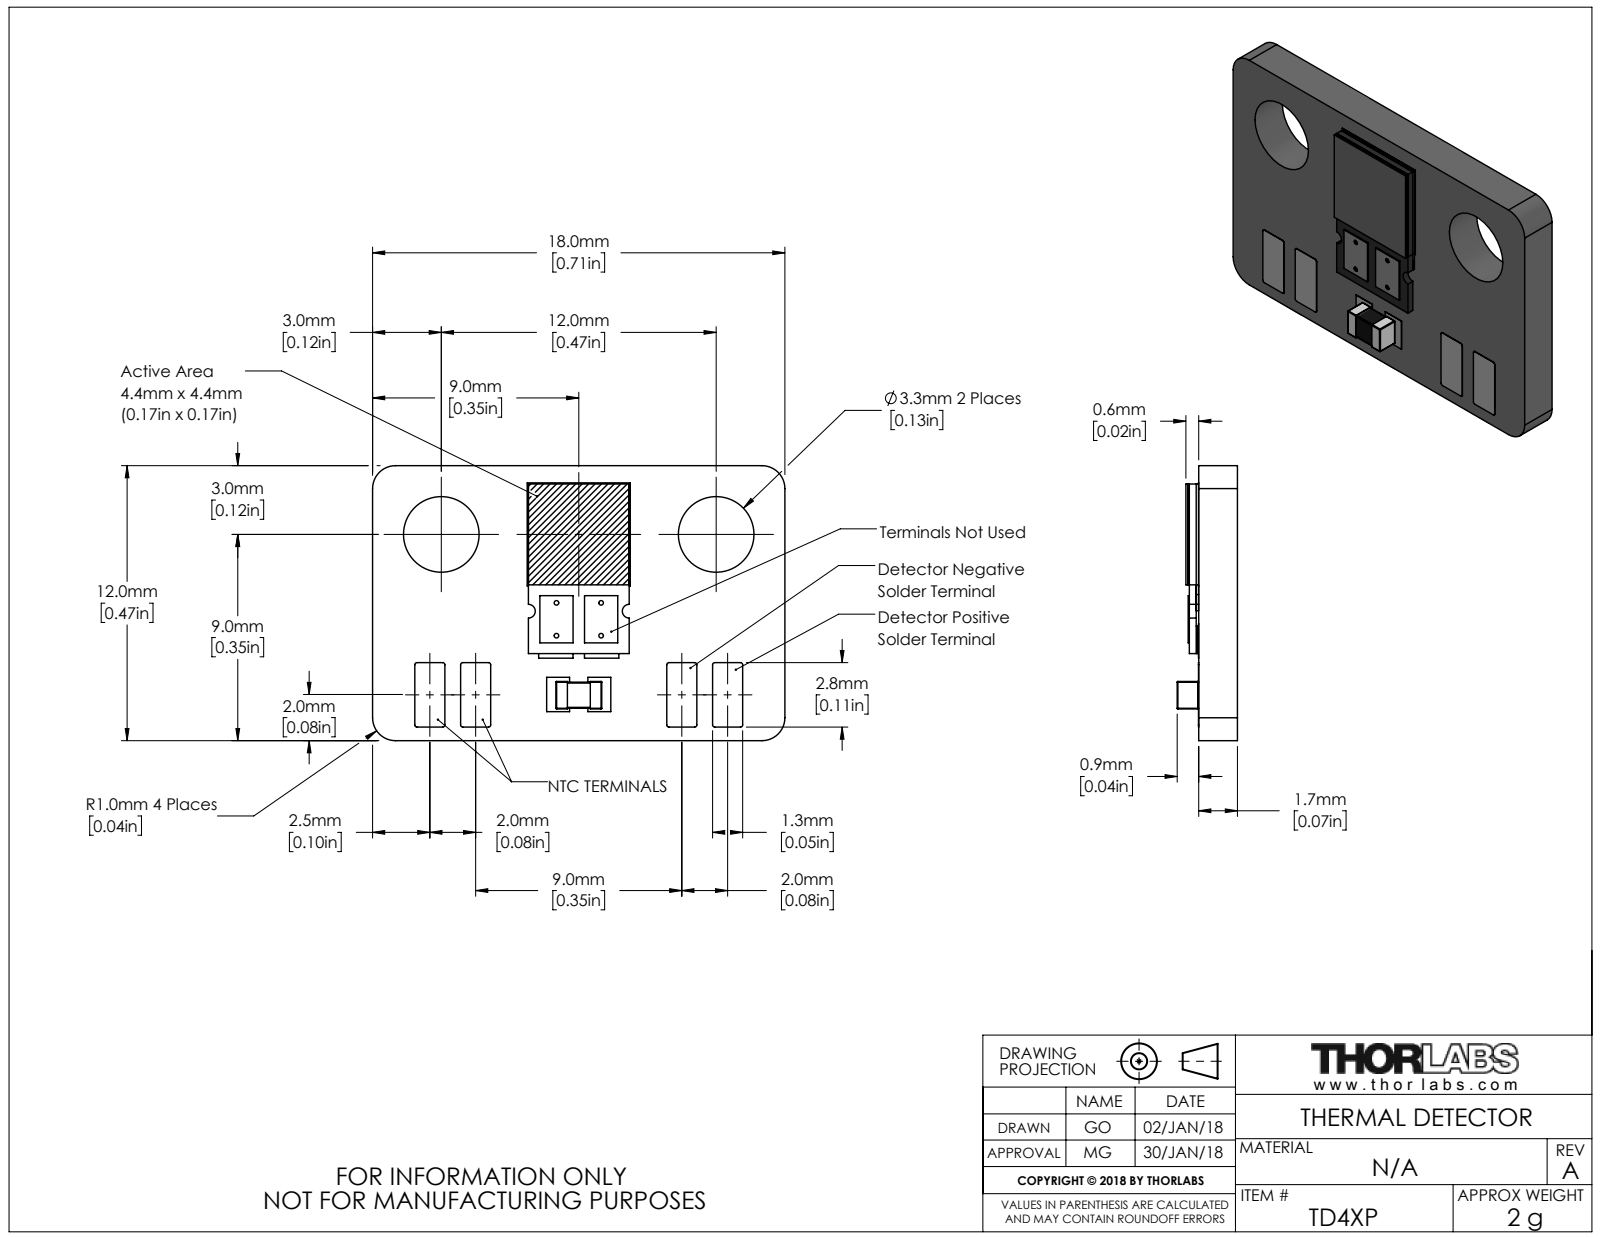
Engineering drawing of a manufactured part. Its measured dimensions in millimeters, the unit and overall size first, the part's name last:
Units: millimetres
Overall size (bounding box): 18 × 12 × 2.63
Round holes (diameter × count): ⌀0.2 ×4, ⌀3.3 ×2
Partial cylindrical surfaces — rounded edges, fillets, slot ends (radius × count): R1 ×4, R0.3 ×2
Main face-to-face distances: 1.69, 1.7, 0.45, 0.4, 1.8, 0.41, 2.1, 0.35, 0.46, 2.15
Hole centre spacings: 1.43, 1.95, 2.42, 5.84, 5.85, 6.69, 6.7, 7.58
Volume: 353 mm³ · Surface area: 849 mm²
Bodies: 19 solids, 214 faces (133 planar, 73 cylindrical, 8 other)
Part name (STEP PRODUCT): B1_PCB_Standard; B1-SC_Standard; NTC_0805; MTN10551-E0W
STEP written by: SolidWorks 2016 (CONFIG_CONTROL_DESIGN)
